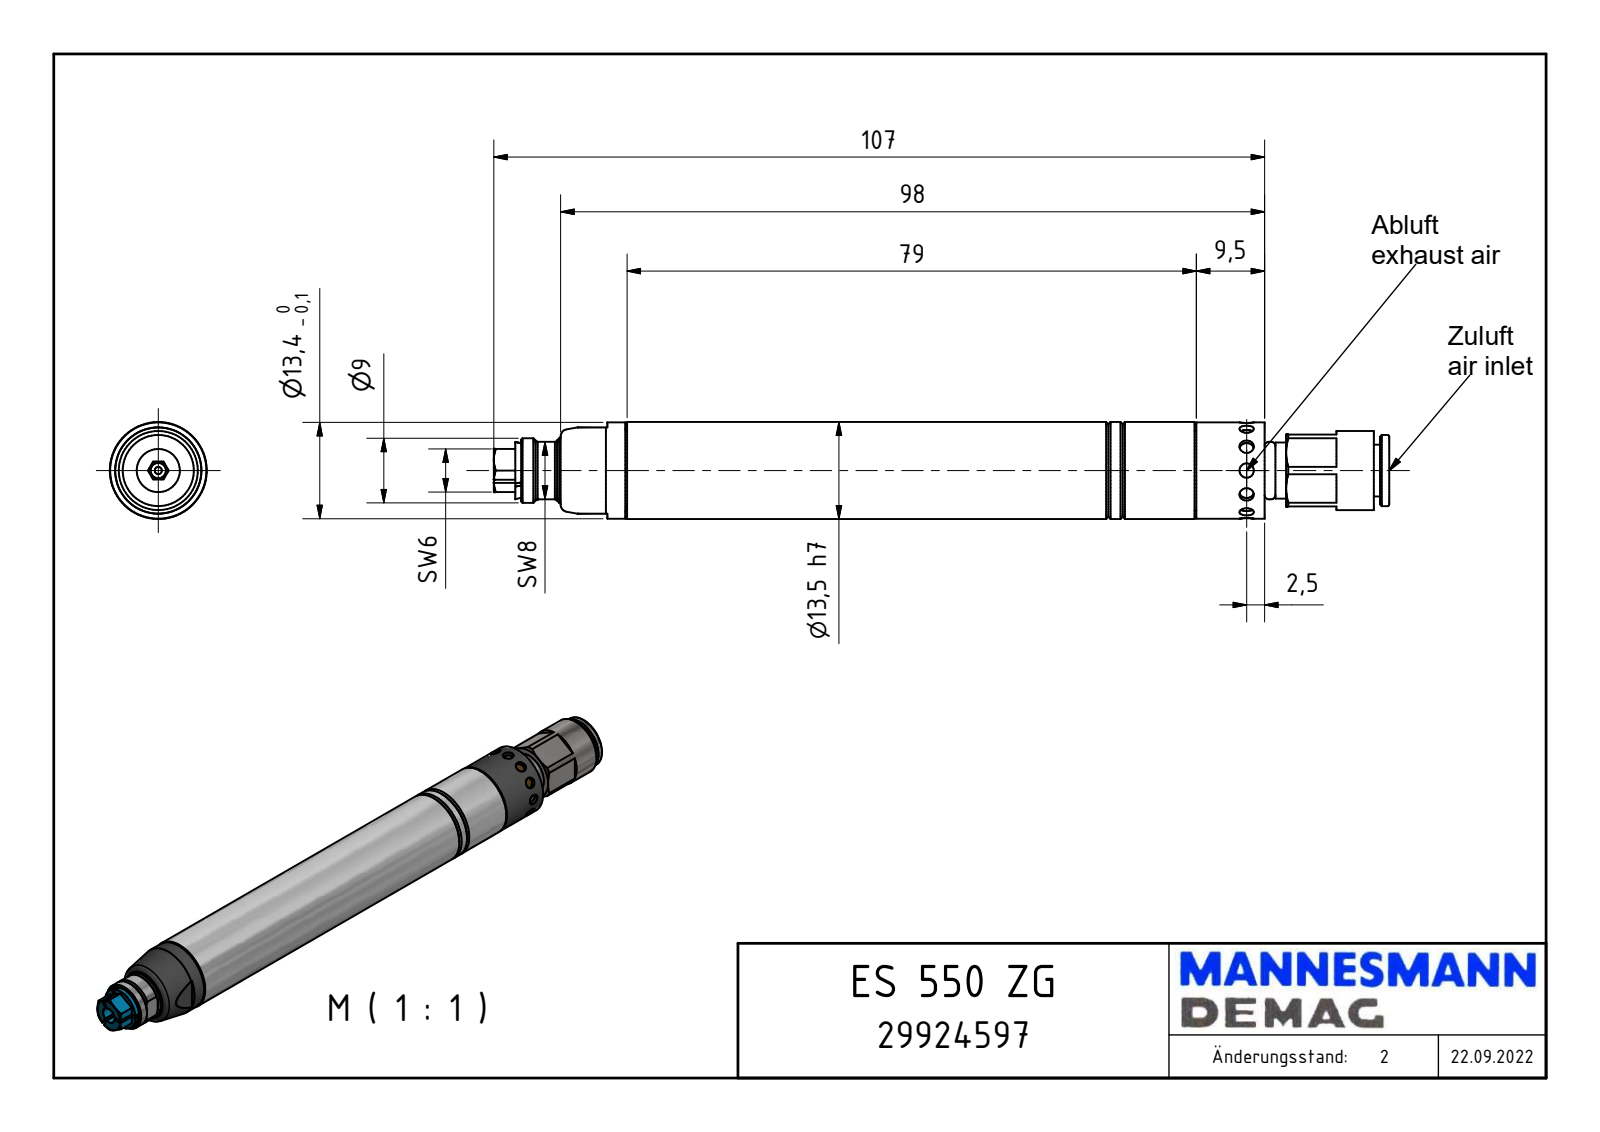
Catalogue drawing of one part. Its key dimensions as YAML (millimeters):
part_name: "ES 550 ZG_29924597"
step_written_by: "Autodesk Inventor 2008 (AUTOMOTIVE_DESIGN)"
units: millimeters
bodies: {solids: 1, faces: 163, planar: 67, cylindrical: 54, other: 42}
overall_size: [124.87, 13.5, 13.5]
volume: 14993
surface_area: 6924
round_holes:
  - {diameter: 2, count: 6}
  - {diameter: 3, count: 1}
  - {diameter: 3.1, count: 1}
  - {diameter: 5, count: 1}
  - {diameter: 6, count: 1}
  - {diameter: 9.5, count: 1}
  - {diameter: 11.2, count: 1}
round_bosses_or_shafts:
  - {diameter: 13.5, count: 1}
  - {diameter: 13.4, count: 1}
  - {diameter: 12.24, count: 1}
  - {diameter: 11.01, count: 1}
  - {diameter: 11, count: 1}
  - {diameter: 10.8, count: 1}
  - {diameter: 9.9, count: 1}
  - {diameter: 9, count: 1}
partial_cylinders:
  - {radius: 5, count: 3}
  - {radius: 6, count: 1}
face_to_face_distances: [10, 4.75, 5.25, 3, 15.21, 0.5, 1.5, 79.25, 1, 17.36]
